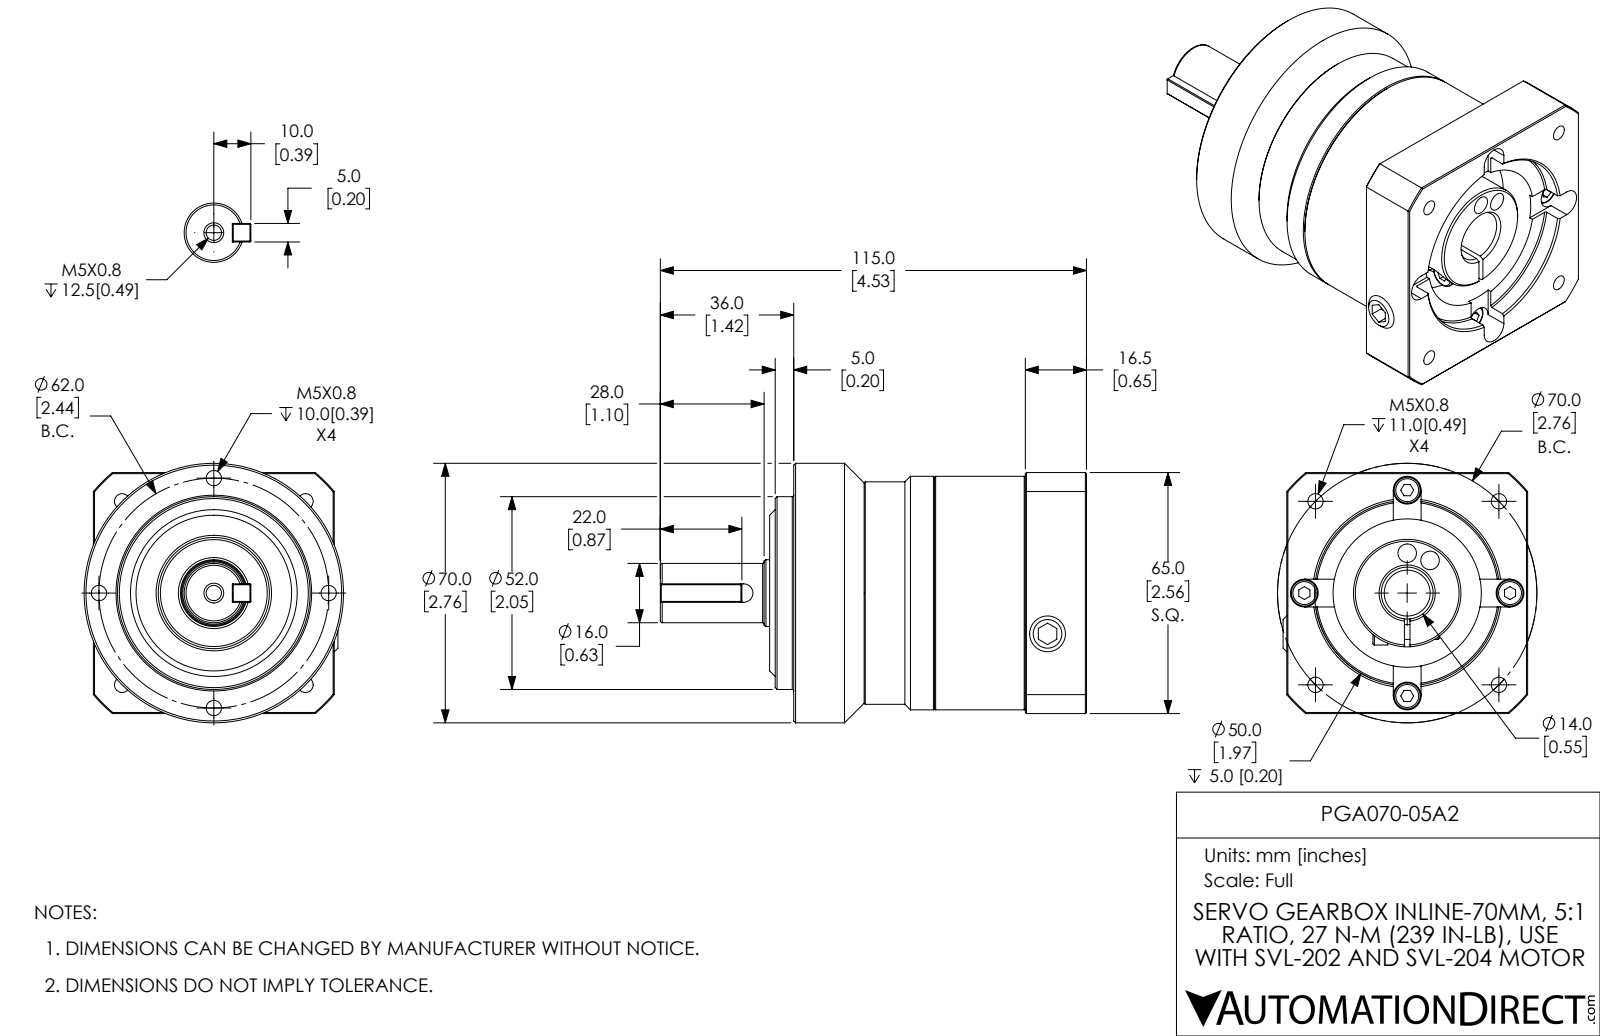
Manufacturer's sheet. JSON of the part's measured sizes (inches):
{"part_name": "PGA070-05A2", "step_written_by": "SolidWorks 2019 (CONFIG_CONTROL_DESIGN)", "units": "inches", "bodies": {"solids": 1, "faces": 310, "planar": 127, "cylindrical": 81, "other": 102}, "overall_size": [4.528, 2.756, 2.756], "volume_in3": 16.11, "surface_area_in2": 58.69, "round_holes": [[0.163, 9], [0.295, 4], [0.197, 2], [0.177, 1], [0.315, 1], [0.551, 1], [1.142, 1], [1.575, 1], [1.969, 1]], "round_bosses_or_shafts": [[0.276, 5], [2.756, 1], [2.48, 1], [2.362, 1], [2.047, 1], [0.709, 1], [0.63, 1], [0.157, 1]], "partial_cylinders_radius": [[0.064, 1], [0.098, 1], [0.157, 1], [1.673, 1]], "face_to_face_distances": [3.11, 2.559, 0.65, 2.461, 0.197, 0.453, 0.256, 3.366, 2.717, 0.059], "hole_center_spacings": [0.981, 1.005, 1.638, 2.285, 2.402, 0.128, 1.093, 1.22]}
